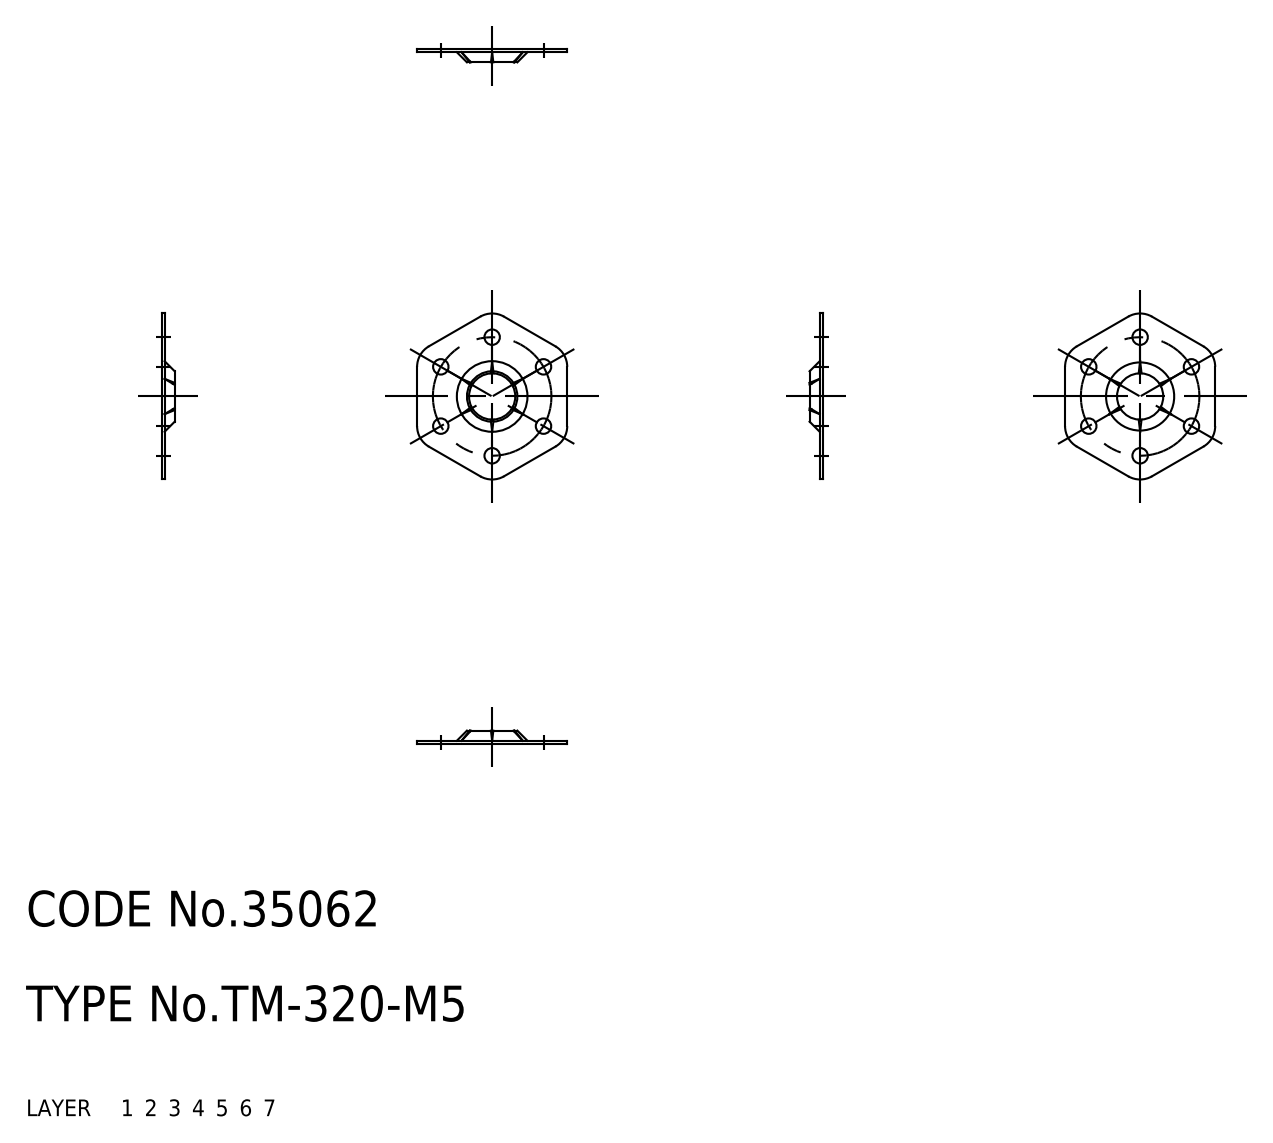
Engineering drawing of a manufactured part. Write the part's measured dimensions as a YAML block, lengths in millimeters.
part_name: "67112180"
step_written_by: "CADfix (AUTOMOTIVE_DESIGN)"
units: millimeters
bodies: {solids: 1, faces: 62, planar: 0, cylindrical: 0, other: 62}
overall_size: [14, 12.66, 1.1]
volume: 30
surface_area: 266
